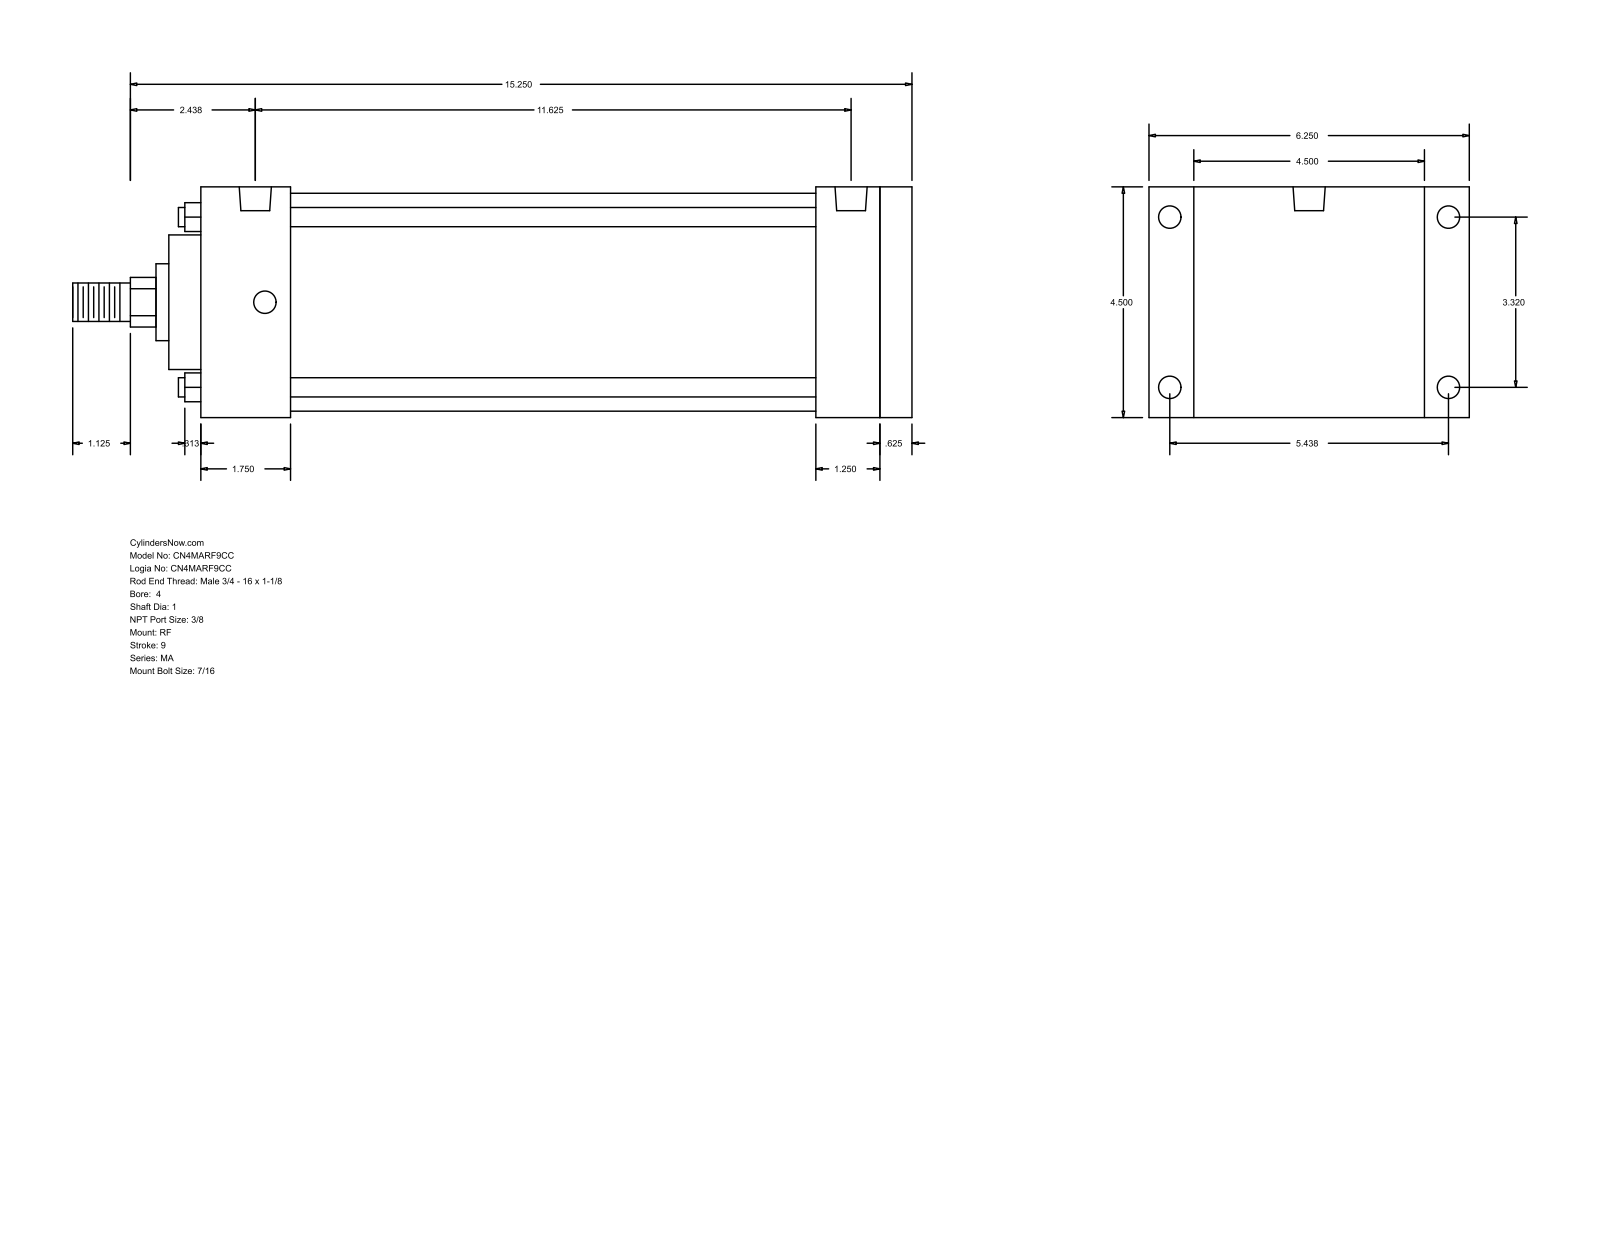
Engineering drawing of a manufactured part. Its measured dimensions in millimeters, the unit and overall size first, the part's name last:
Units: millimetres
Overall size (bounding box): 415.93 × 158.75 × 114.3
Round holes (diameter × count): ⌀11.11 ×8, ⌀15.93 ×2
Round bosses / shafts (diameter × count): ⌀9.53 ×4, ⌀107.95 ×1, ⌀66.67 ×1, ⌀38.1 ×1, ⌀25.4 ×1, ⌀19.05 ×1
Partial cylindrical surfaces — rounded edges, fillets, slot ends (radius × count): R12.29 ×1
Main face-to-face distances: 114.3, 352.43, 15.87, 336.56, 47.62, 22.23, 136.53, 304.81, 31.75, 44.46
Hole centre spacings: 4.76, 84.32, 138.12, 161.82, 285.76, 290.52, 295.28
Bodies: 0 solids, 94 faces (65 planar, 29 cylindrical, 0 other)
Part name (STEP PRODUCT): MA_RF__0400_1
STEP written by: GSSL Pune (CONFIG_CONTROL_DESIGN)
